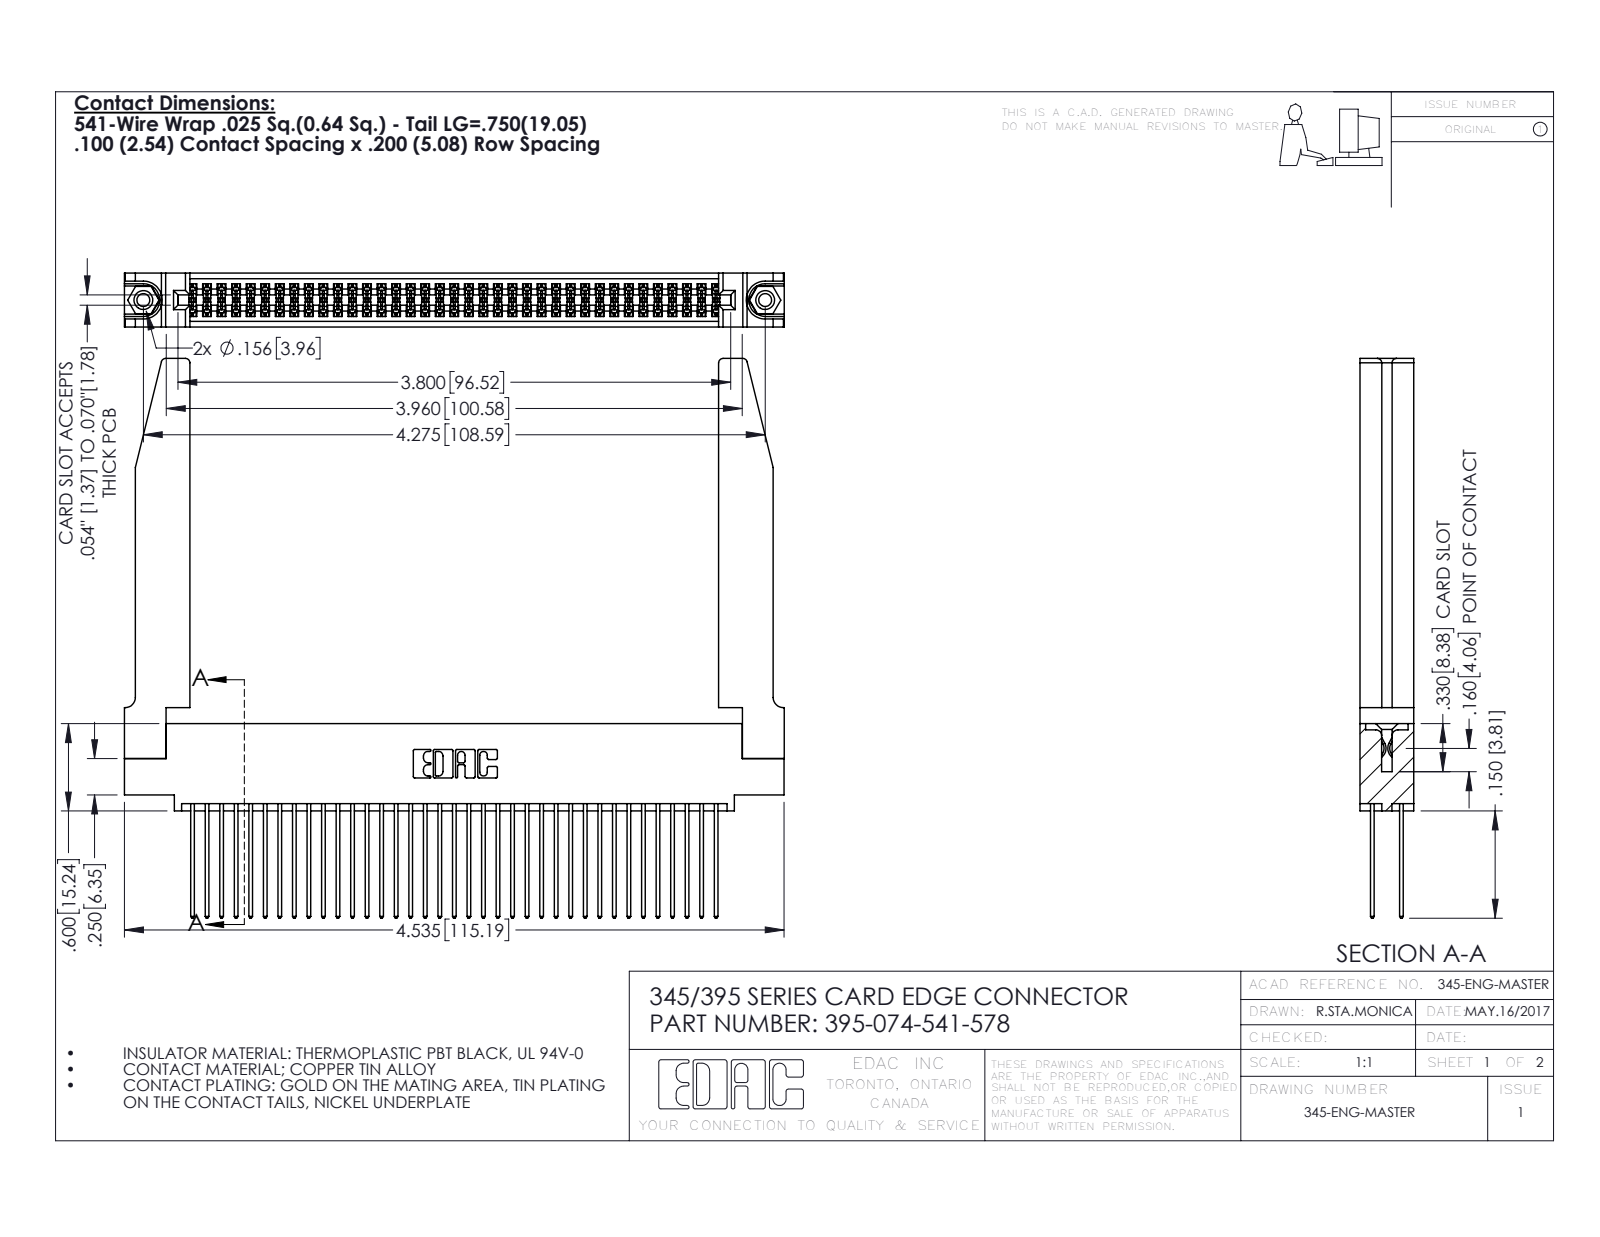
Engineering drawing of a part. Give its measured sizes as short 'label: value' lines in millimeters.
name: 345-250-001_345-250-001-102; 395-074-541-578; 345-220-078_345-220-078; 345-292-001_345-293-141 (+1 more)
written by: SolidWorks 2016 (CONFIG_CONTROL_DESIGN)
unit: mm
bodies: 79 solids, 4064 faces (2668 planar, 1344 cylindrical, 52 other)
size: 115.2 × 97.7 × 9.4
volume: 19 270 mm³; area: 25 830 mm²
holes: 2× ⌀2.3, 2× ⌀3.2, 2× ⌀4, 1× ⌀1.6
bosses: 2× ⌀3.9
rounds: 111× R0.2, 74× R0.3, 22× R0.3, 8× R0.8, 6× R0.2, 6× R0.8, 3× R0.7, 2× R0.4
face distances: 1.8, 7.6, 9.4, 2.5, 6.9, 0.6, 5.1, 5.7, 4.4, 3.8
hole spacings: 6.9, 102.6, 108.6
